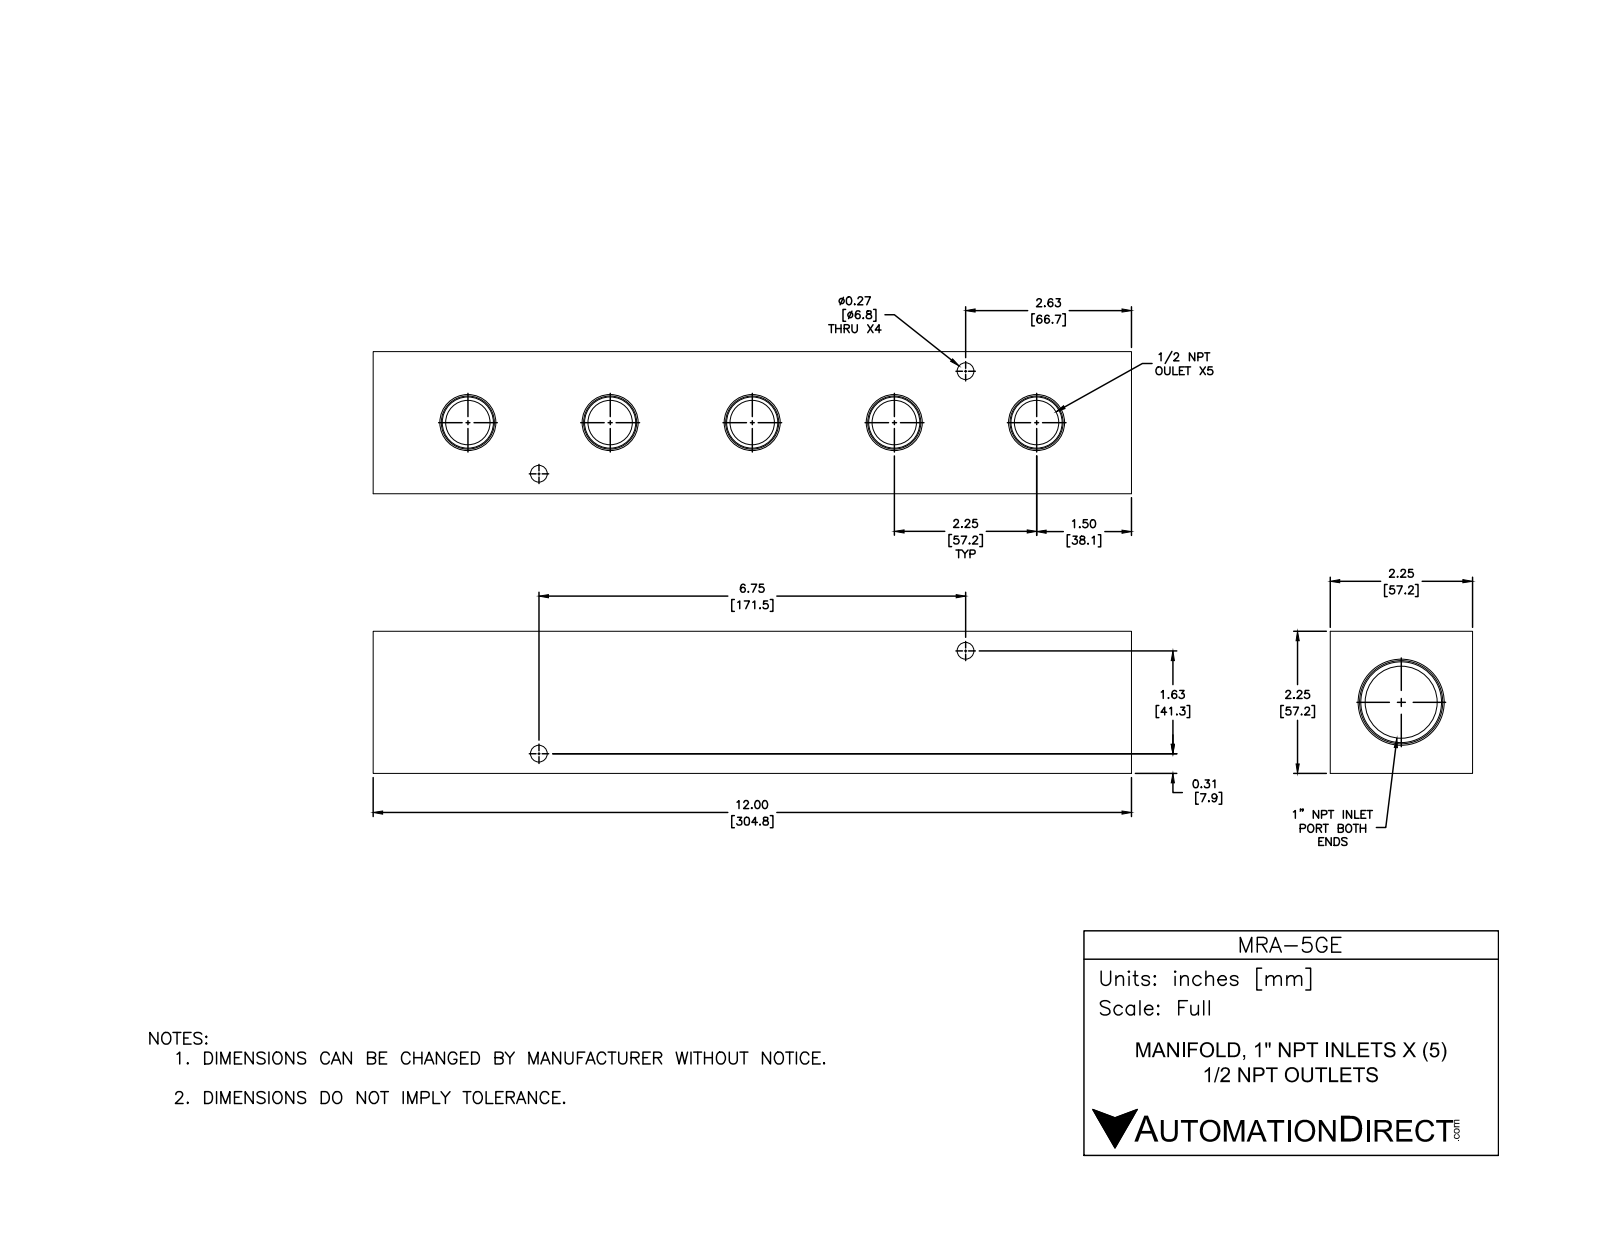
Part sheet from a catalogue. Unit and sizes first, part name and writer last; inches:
Units: inches
Overall size (bounding box): 12 × 2.25 × 2.25
Round holes (diameter × count): ⌀0.703 ×5, ⌀0.266 ×4, ⌀1.141 ×1
Main face-to-face distances: 2.25, 12, 1.72, 0.53, 0.66, 11.34, 10.68
Hole centre spacings: 1.388, 2.25, 4.5, 6.75, 6.943, 3.471, 3.472, 5.683
Volume: 46.08 in³ · Surface area: 169.4 in²
Bodies: 1 solid, 69 faces (13 planar, 28 cylindrical, 28 other)
Part name (STEP PRODUCT): MRA-5GE
STEP written by: SolidWorks 2015 (CONFIG_CONTROL_DESIGN)
